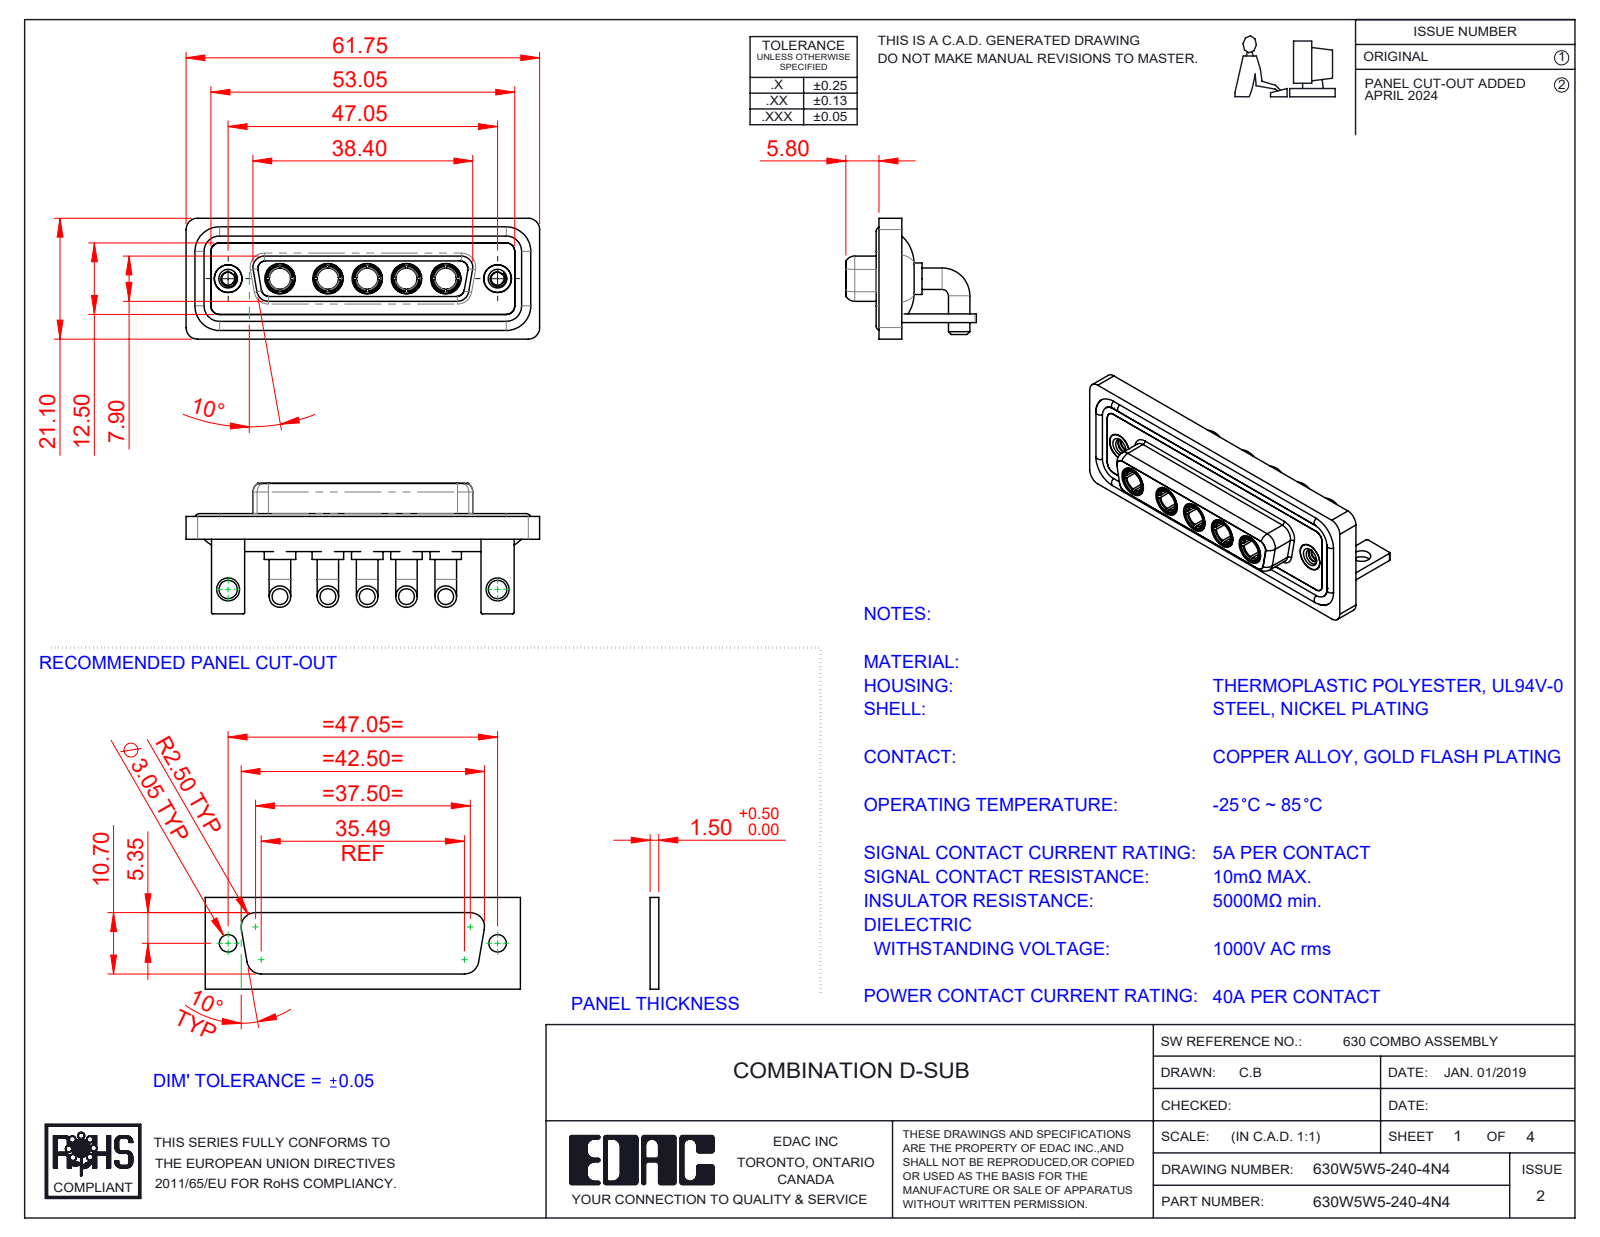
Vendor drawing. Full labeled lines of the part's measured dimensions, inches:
Part name (STEP PRODUCT): 630W5W5-240-4N4; 630Combo Threaded Rivet_2; 630Combo Stabilizer Bracket_50 Contacts; Power Socket_40A RA (+4 more)
STEP written by: SolidWorks 2023 (CONFIG_CONTROL_DESIGN)
Units: inches
Bodies: 19 solids, 824 faces (270 planar, 337 cylindrical, 217 other)
Overall size (bounding box): 2.431 × 0.898 × 0.831
Volume: 0.559 in³ · Surface area: 22.89 in²
Round holes (diameter × count): ⌀0.191 ×7, ⌀0.146 ×5, ⌀0.209 ×5, ⌀0.089 ×2, ⌀0.126 ×2, ⌀0.157 ×2, ⌀0.159 ×2, ⌀0.197 ×2
Round bosses / shafts (diameter × count): ⌀0.148 ×10, ⌀0.217 ×5, ⌀0.205 ×5, ⌀0.195 ×5, ⌀0.187 ×5, ⌀0.063 ×4, ⌀0.195 ×2, ⌀0.189 ×2
Partial cylindrical surfaces — rounded edges, fillets, slot ends (radius × count): R0.079 ×19, R0.059 ×18, R0.01 ×16, R0.053 ×8, R0.063 ×8, R0.02 ×5, R0.083 ×5, R0.024 ×4
Main face-to-face distances: 0.016, 0.071, 0.114, 0.146, 0.059, 0.161, 0.043, 0.055, 0.063, 0.098
Hole centre spacings: 0.27, 0.356, 1.496, 1.852, 0.27, 0.33, 0.54, 0.541
